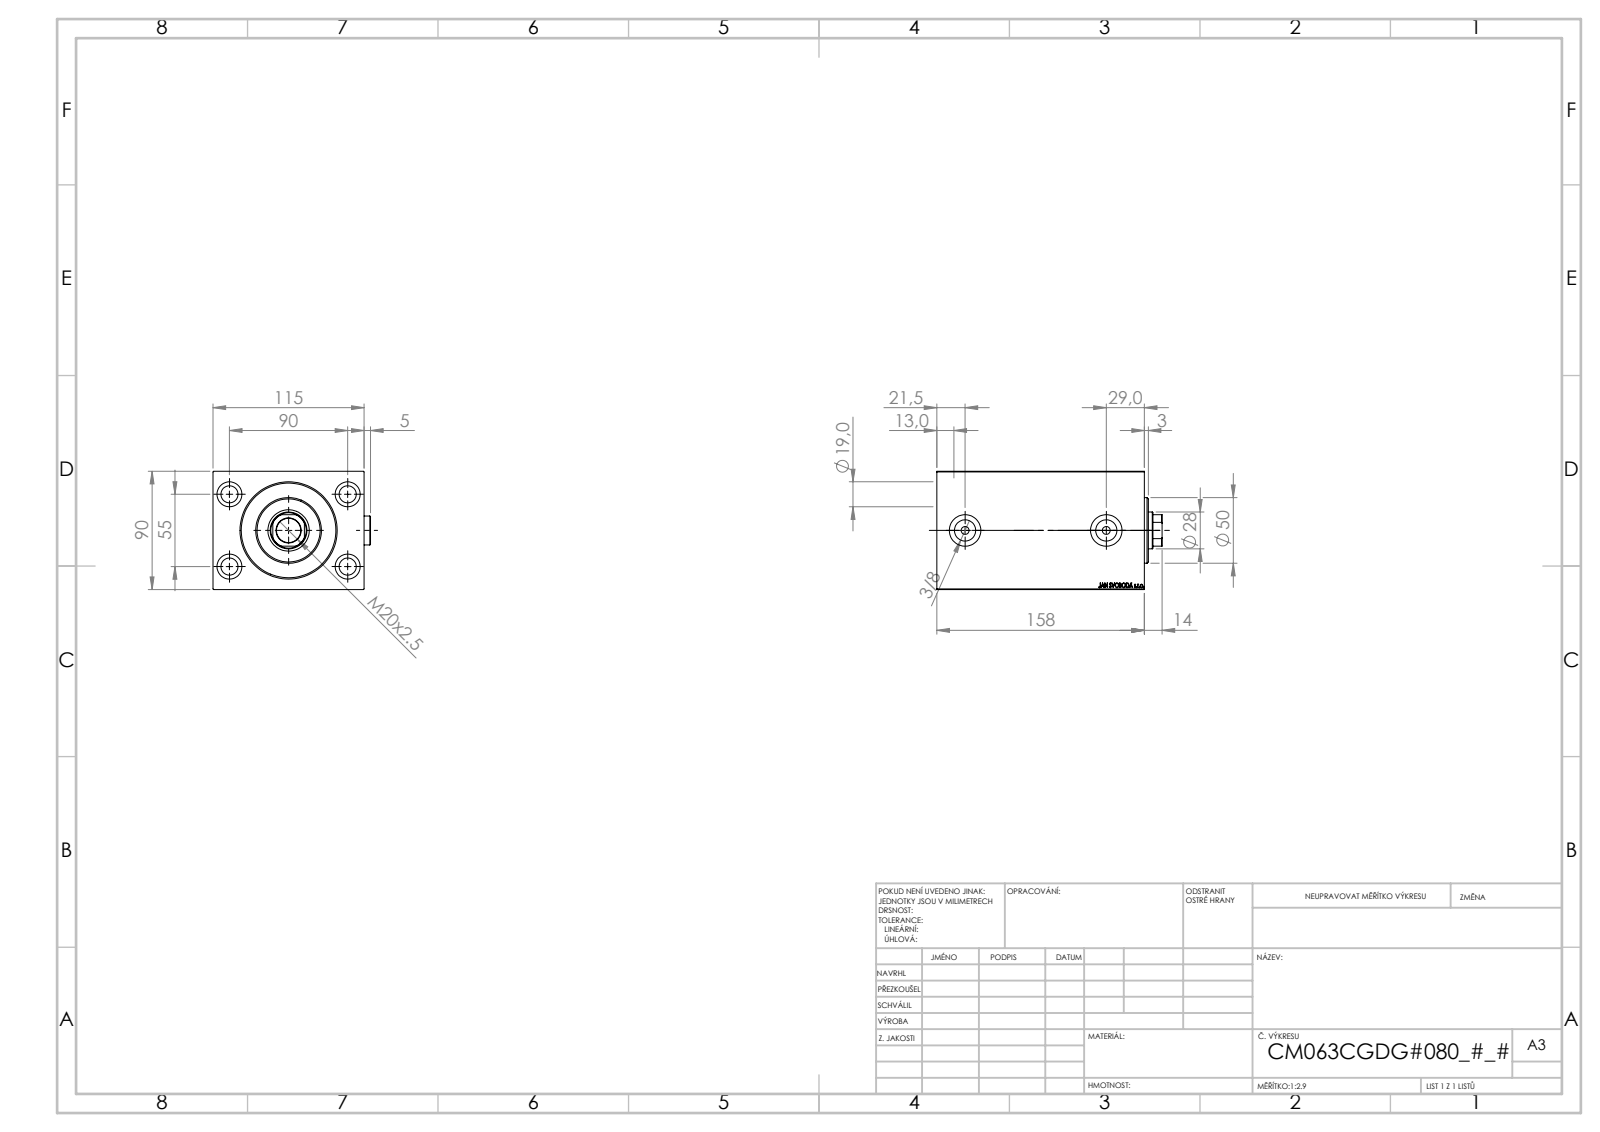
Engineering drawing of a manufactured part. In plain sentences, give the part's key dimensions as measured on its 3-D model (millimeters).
The part is named "Zatka_OIL_PORT; V450CM_VC_B; V450CM_C_Body; V450CM_C_VCP". Its 3-D file was written by "SolidWorks 2019 (CONFIG_CONTROL_DESIGN)". It is 5 solids with 919 faces: 443 planar, 78 cylindrical and 398 other. Overall it measures 171.5 by 119.9 by 90 millimeters. Its volume is 1 331 000 cubic millimeters and its surface area 183 755 square millimeters. Round holes: 4 of diameter 13, 4 of diameter 19, 2 of diameter 6, 2 of diameter 16.17, 2 of diameter 24, 1 of diameter 18.5, 1 of diameter 28, 1 of diameter 31.5, 1 of diameter 63, 1 of diameter 65, 1 of diameter 72. Round bosses or shafts: 2 of diameter 22, 1 of diameter 50. Partial cylindrical surfaces (rounded edges, fillets, slot ends): 1 of radius 13.5. The main face-to-face distances are 90, 115, 158, 17.5, 140.5, 13.5, 127, 144.5, 64.5, 80. The hole center spacings are 52.74, 55, 90, 105.48, 107.5.
